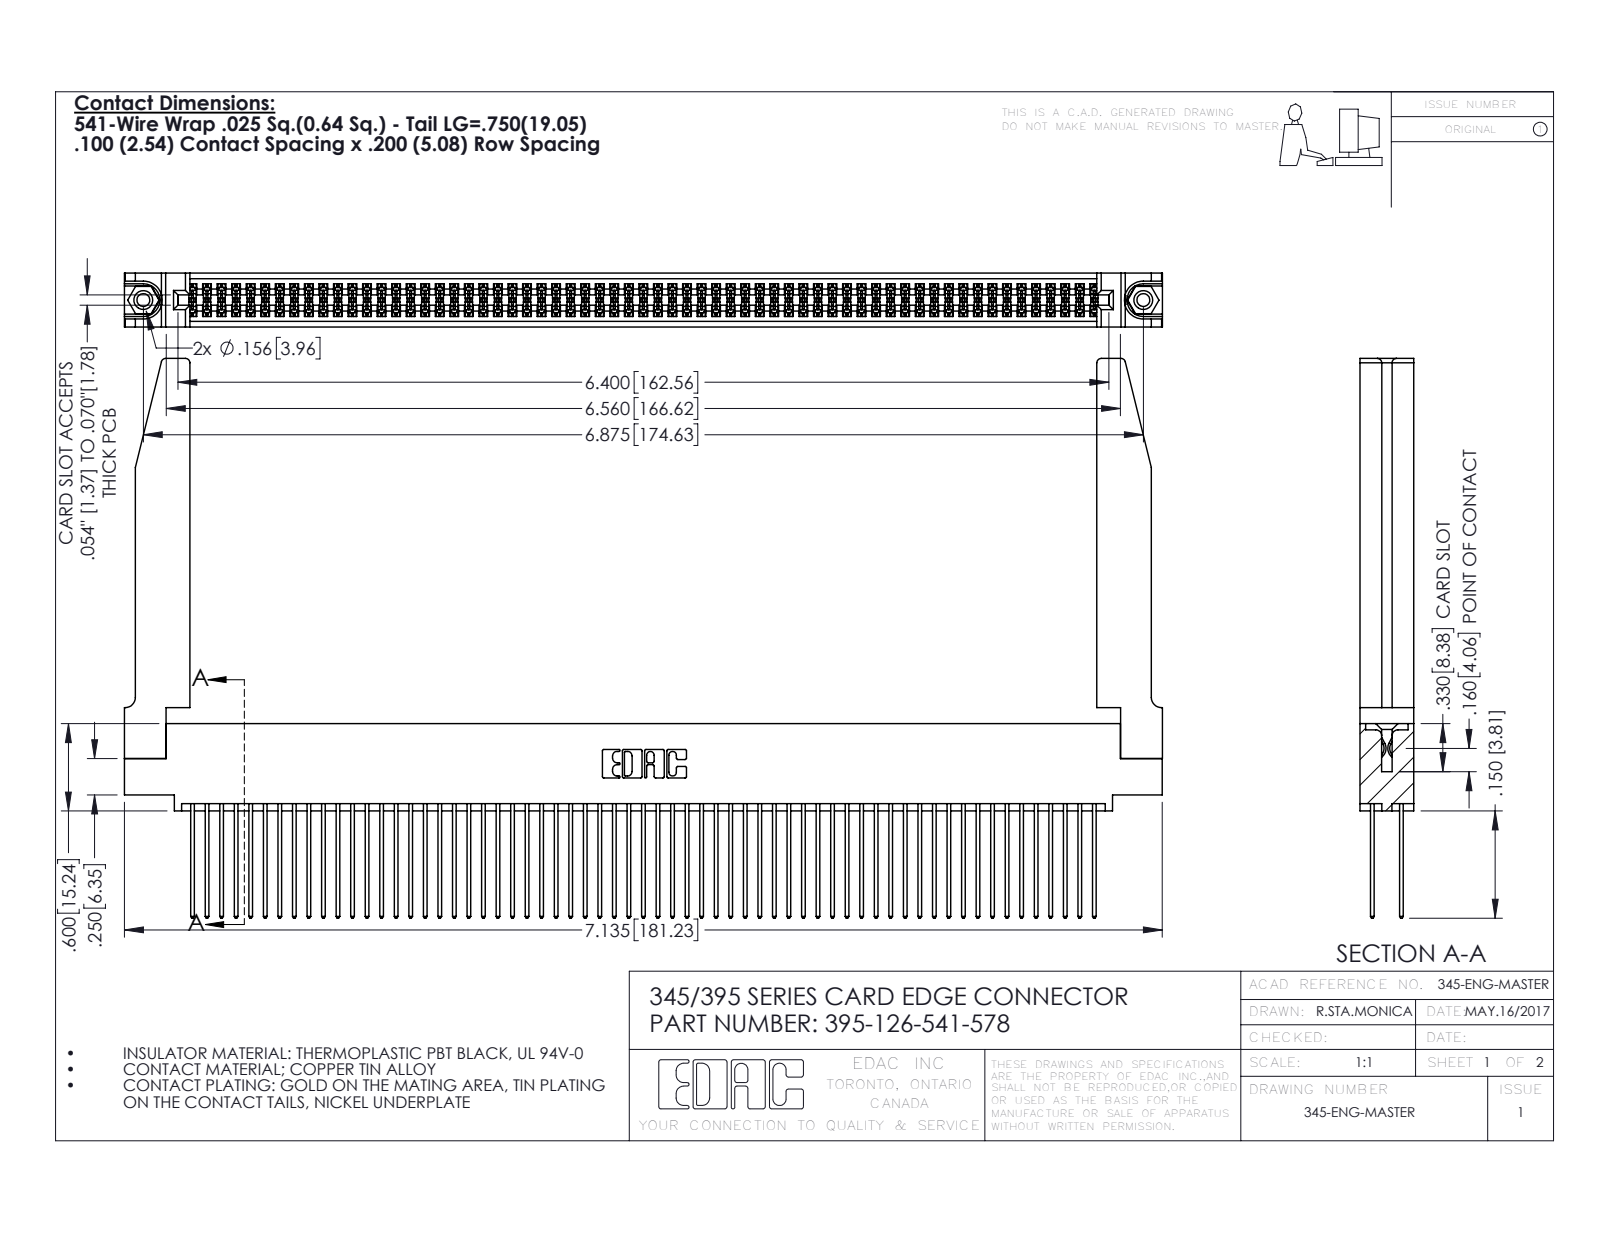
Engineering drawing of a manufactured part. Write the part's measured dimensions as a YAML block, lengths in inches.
part_name: "345-250-001_345-250-001-102; 345 Part_0.110 Offset - 0.156 Dia-TH; 345-292-001_345-293-141; 345-220-078_345-220-078 (+1 more)"
step_written_by: "SolidWorks 2016 (CONFIG_CONTROL_DESIGN)"
units: inches
bodies: {solids: 131, faces: 6664, planar: 4384, cylindrical: 2228, other: 52}
overall_size: [7.136, 3.847, 0.37]
volume: 1.6
surface_area: 58.92
round_holes:
  - {diameter: 0.089, count: 2}
  - {diameter: 0.125, count: 2}
  - {diameter: 0.156, count: 2}
  - {diameter: 0.064, count: 1}
round_bosses_or_shafts:
  - {diameter: 0.155, count: 2}
partial_cylinders:
  - {radius: 0.006, count: 189}
  - {radius: 0.01, count: 126}
  - {radius: 0.01, count: 22}
  - {radius: 0.03, count: 8}
  - {radius: 0.007, count: 6}
  - {radius: 0.031, count: 6}
  - {radius: 0.026, count: 3}
  - {radius: 0.014, count: 2}
face_to_face_distances: [0.072, 0.298, 0.2, 0.098, 0.272, 0.025, 0.37, 0.225, 0.175, 0.148]
hole_center_spacings: [0.27, 6.639, 6.875]
